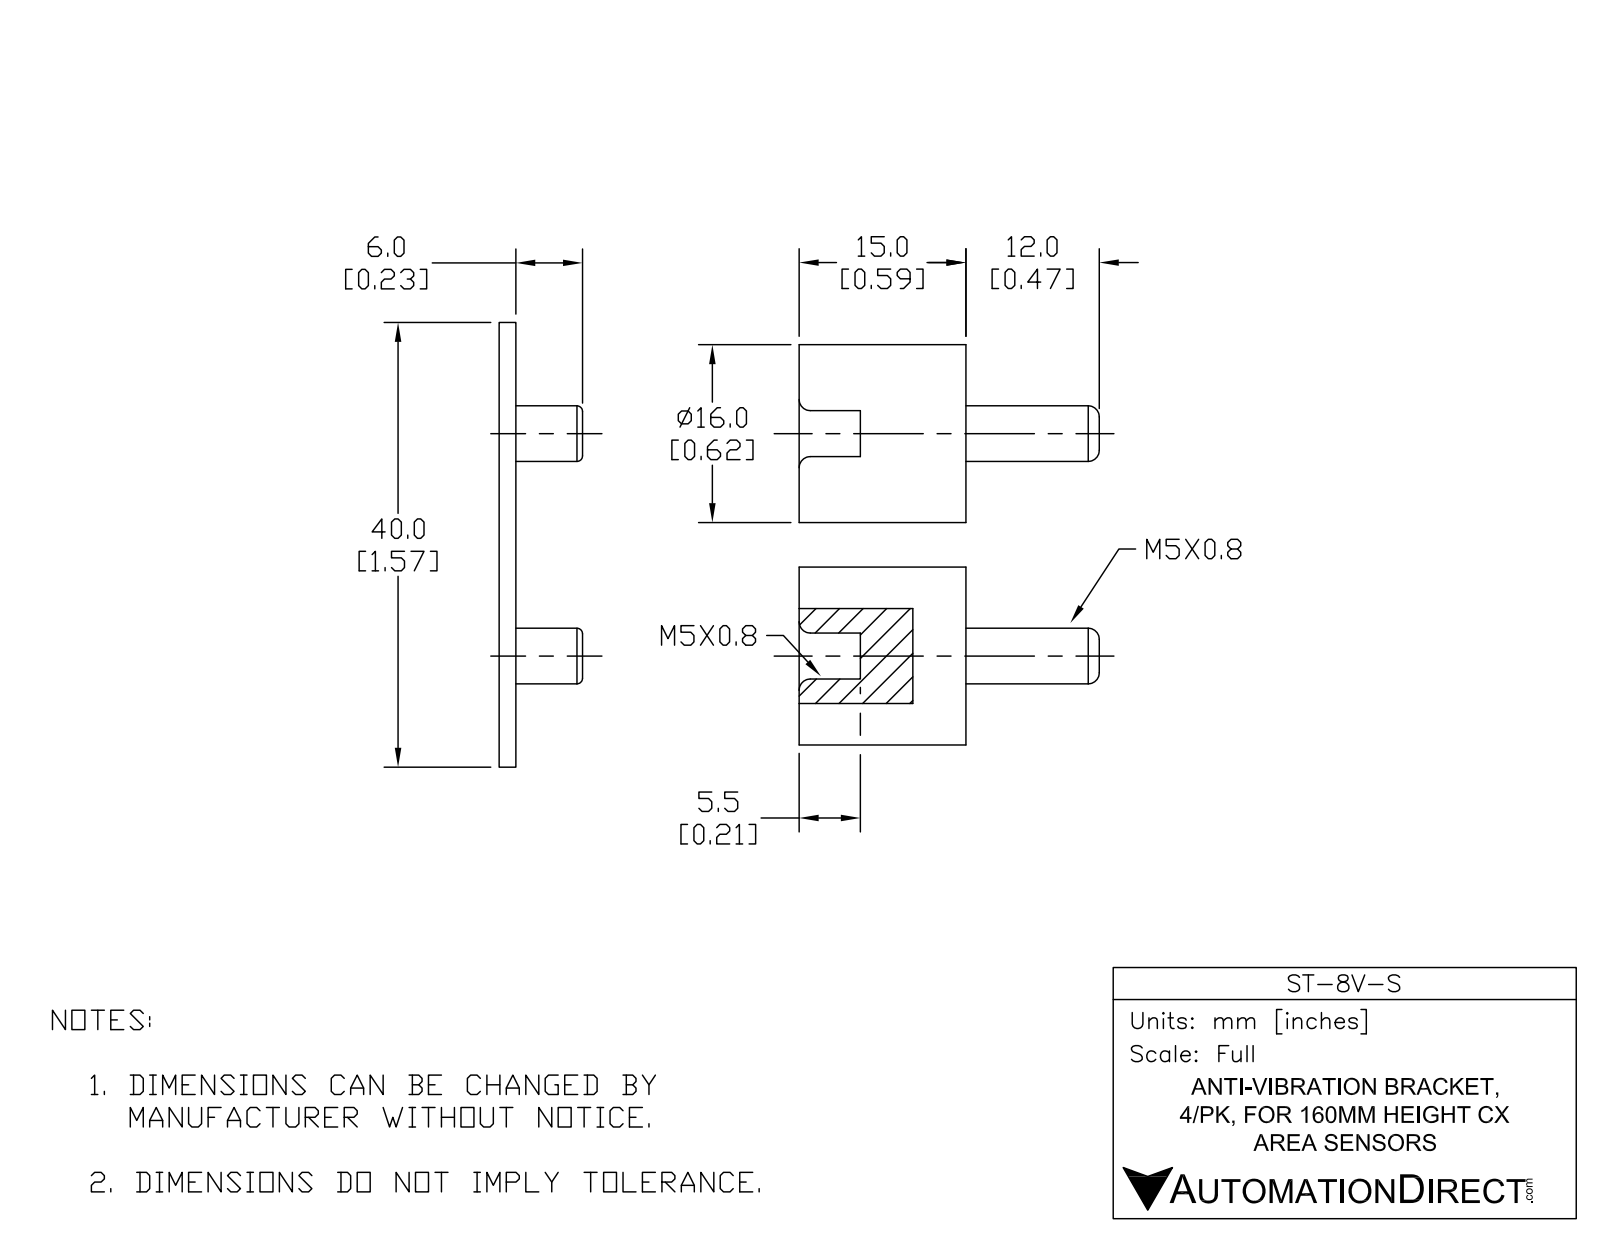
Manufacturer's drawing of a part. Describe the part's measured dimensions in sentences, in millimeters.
The part is named "SAV_EOS_ANTIVIB-3DSOLID_2083". Its 3-D file was written by "unknown (AUTOMOTIVE_DESIGN)". It is 3 solids with 30 faces: 16 planar, 8 cylindrical and 6 other. Overall it measures 46.19 by 40 by 16 millimeters. Its volume is 7 177 cubic millimeters and its surface area 3 939 square millimeters. Round holes: 2 of diameter 4.13. Round bosses or shafts: 2 of diameter 16, 2 of diameter 5. The main face-to-face distances are 34.19, 32.69, 1.5, 15, 17.69, 19.19, 10, 9.5, 5.5, 23.19. The hole center spacings are 20.
